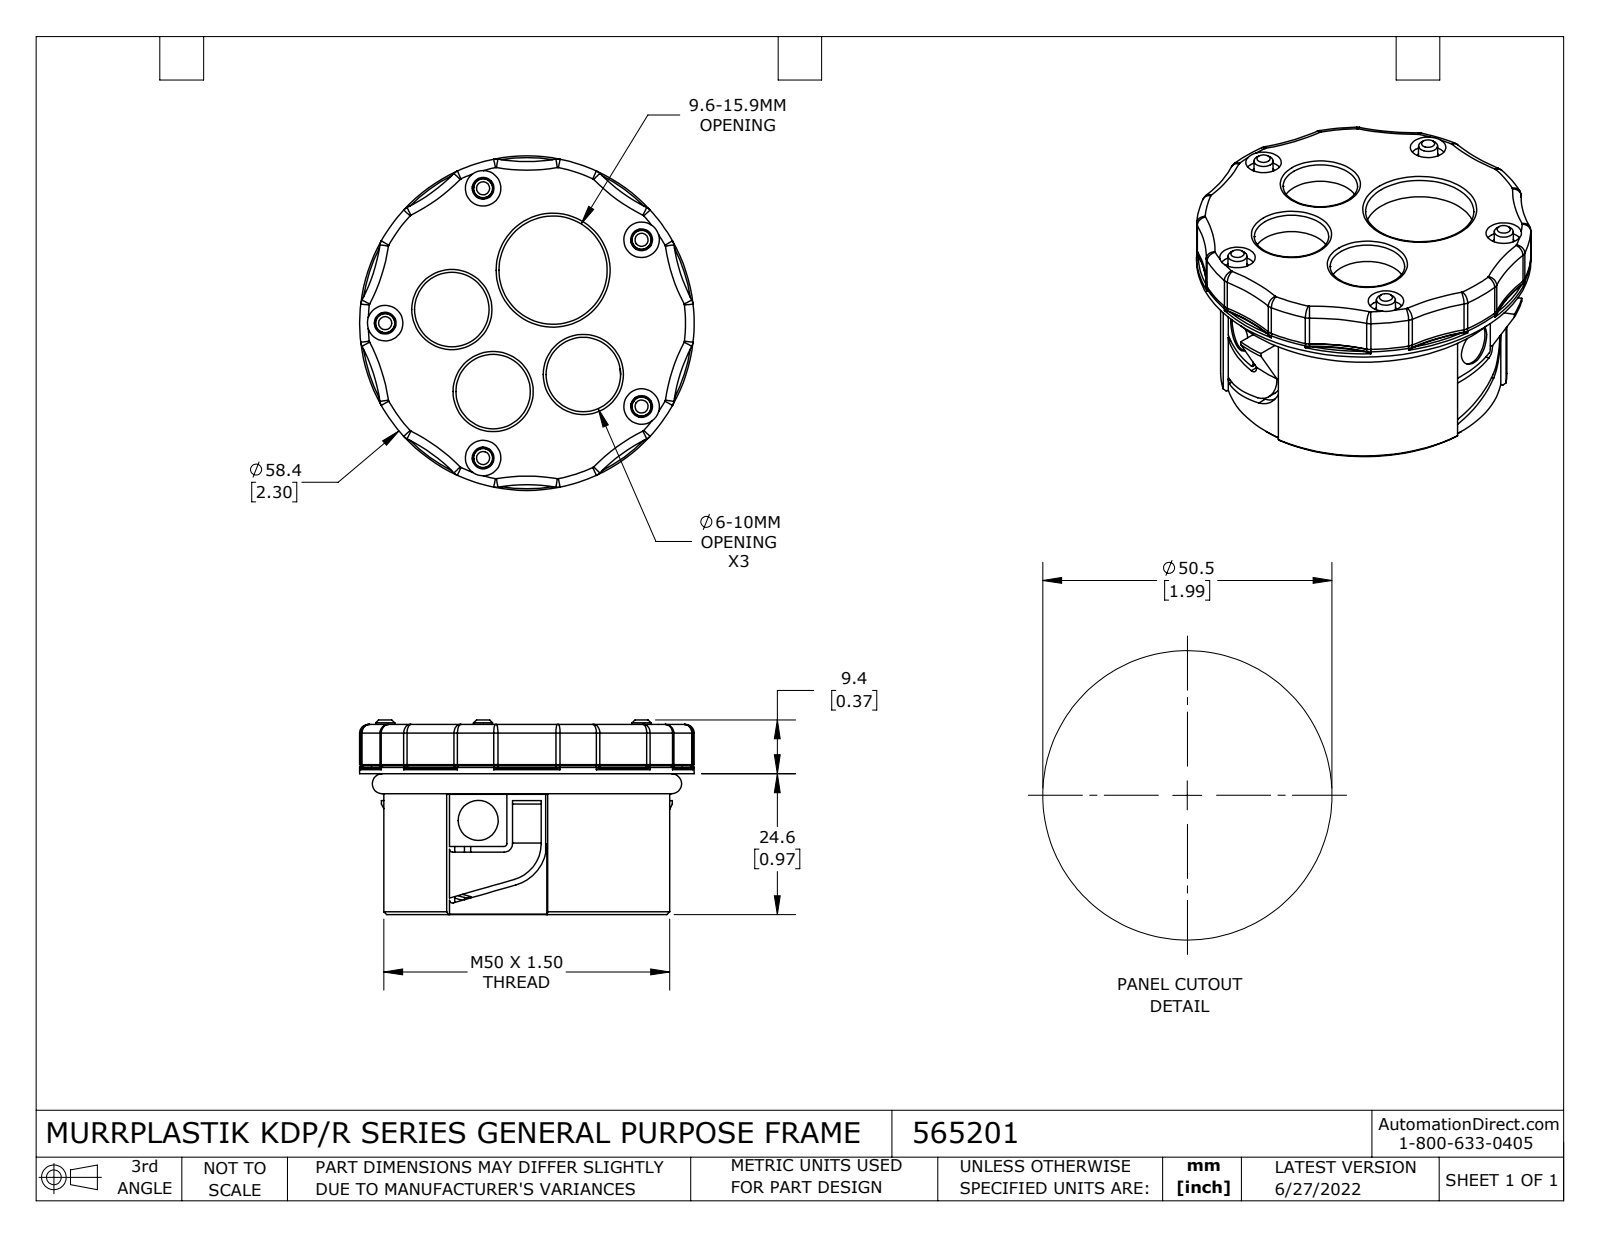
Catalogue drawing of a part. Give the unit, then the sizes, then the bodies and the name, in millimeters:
Units: millimetres
Overall size (bounding box): 58.4 × 58.4 × 34
Round holes (diameter × count): ⌀3.8 ×8, ⌀6.2 ×5, ⌀7 ×3, ⌀13 ×3, ⌀18.9 ×1, ⌀43.4 ×1, ⌀45 ×1, ⌀54.4 ×1
Round bosses / shafts (diameter × count): ⌀58.4 ×1, ⌀53.4 ×1, ⌀51 ×1, ⌀50 ×1, ⌀48.7 ×1, ⌀46 ×1, ⌀44.2 ×1, ⌀41.71 ×1
Partial cylindrical surfaces — rounded edges, fillets, slot ends (radius × count): R2 ×20, R30 ×10, R0.3 ×6, R0.5 ×5, R1.5 ×3, R6.5 ×3, R7.5 ×3, R1.75 ×2
Main face-to-face distances: 1.75, 3.5, 4, 7.5, 5.75, 8.2, 4.7, 6.45, 12.2, 1.1
Hole centre spacings: 24.75, 19.75, 29.1, 47.08, 13.32, 16.03, 18.96, 29.09
Volume: 30 460 mm³ · Surface area: 30 735 mm²
Bodies: 6 solids, 491 faces (90 planar, 195 cylindrical, 206 other)
Part name (STEP PRODUCT): 565201
STEP written by: SolidWorks 2021 (CONFIG_CONTROL_DESIGN)
